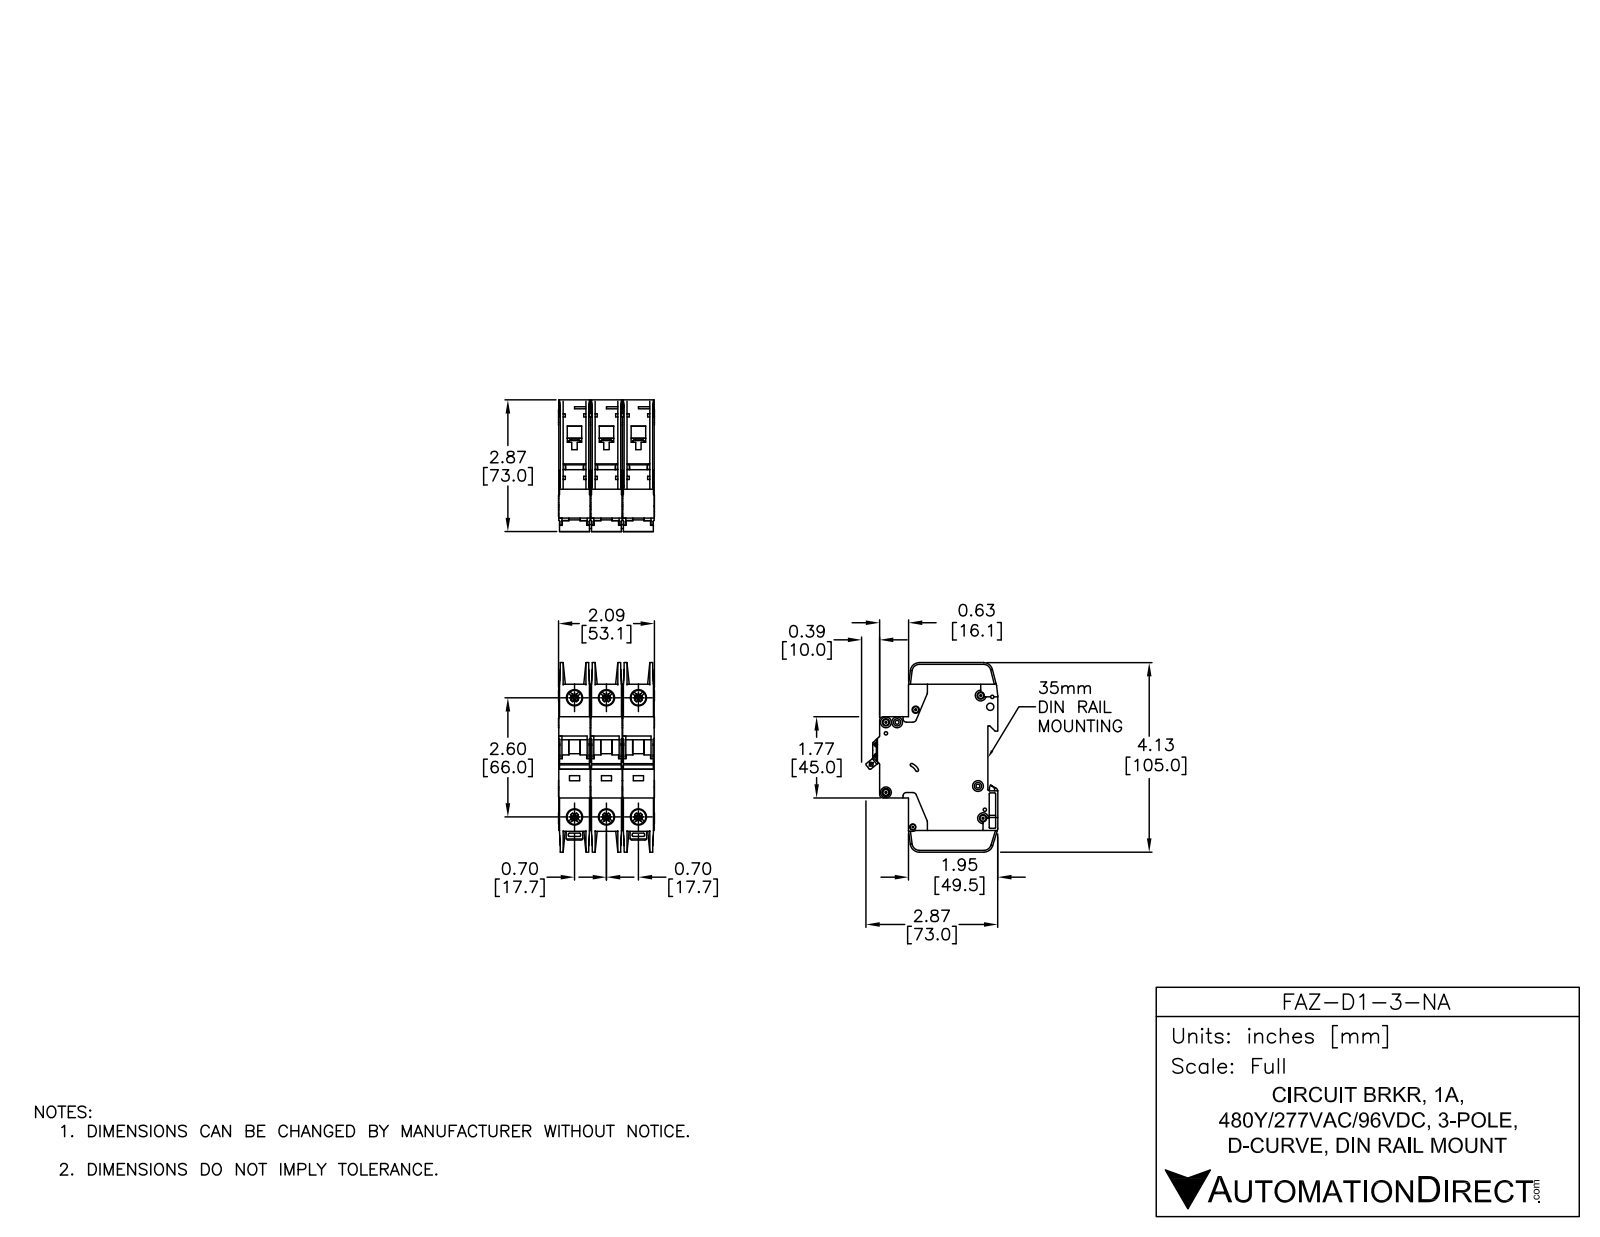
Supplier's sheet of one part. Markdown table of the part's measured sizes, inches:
| quantity | value |
| --- | --- |
| part name | FAZ-D1-3-NA |
| STEP written by | SolidWorks 2014 (AUTOMOTIVE_DESIGN) |
| units | inches |
| bodies | 9 solids, 2352 faces (1227 planar, 789 cylindrical, 336 other) |
| overall size | 4.134 × 2.876 × 2.091 |
| volume | 14.22 in³ |
| surface area | 115 in² |
| round holes (diameter × count) | 0.142 × 7, 0.281 × 6, 0.323 × 6, 0.043 × 2, 0.059 × 2, 0.157 × 2, 0.075 × 1, 0.085 × 1, 0.087 × 1, 0.1 × 1, 0.13 × 1, 0.134 × 1 |
| round bosses / shafts (diameter × count) | 0.236 × 7, 0.098 × 3 |
| partial cylindrical surfaces (radius × count) | 0.01 × 65, 0.02 × 30, 0.039 × 26, 0.079 × 14, 0.071 × 5, 0.197 × 5, 0.157 × 4, 0.008 × 2 |
| main face-to-face distances | 0.697, 1.394, 0.689, 1.386, 0.028, 0.593, 0.096, 0.069, 0.62, 0.524 |
| hole center spacings | 0.697, 2.69, 2.598, 0.244, 1.394, 2.948, 0.204, 0.24 |
